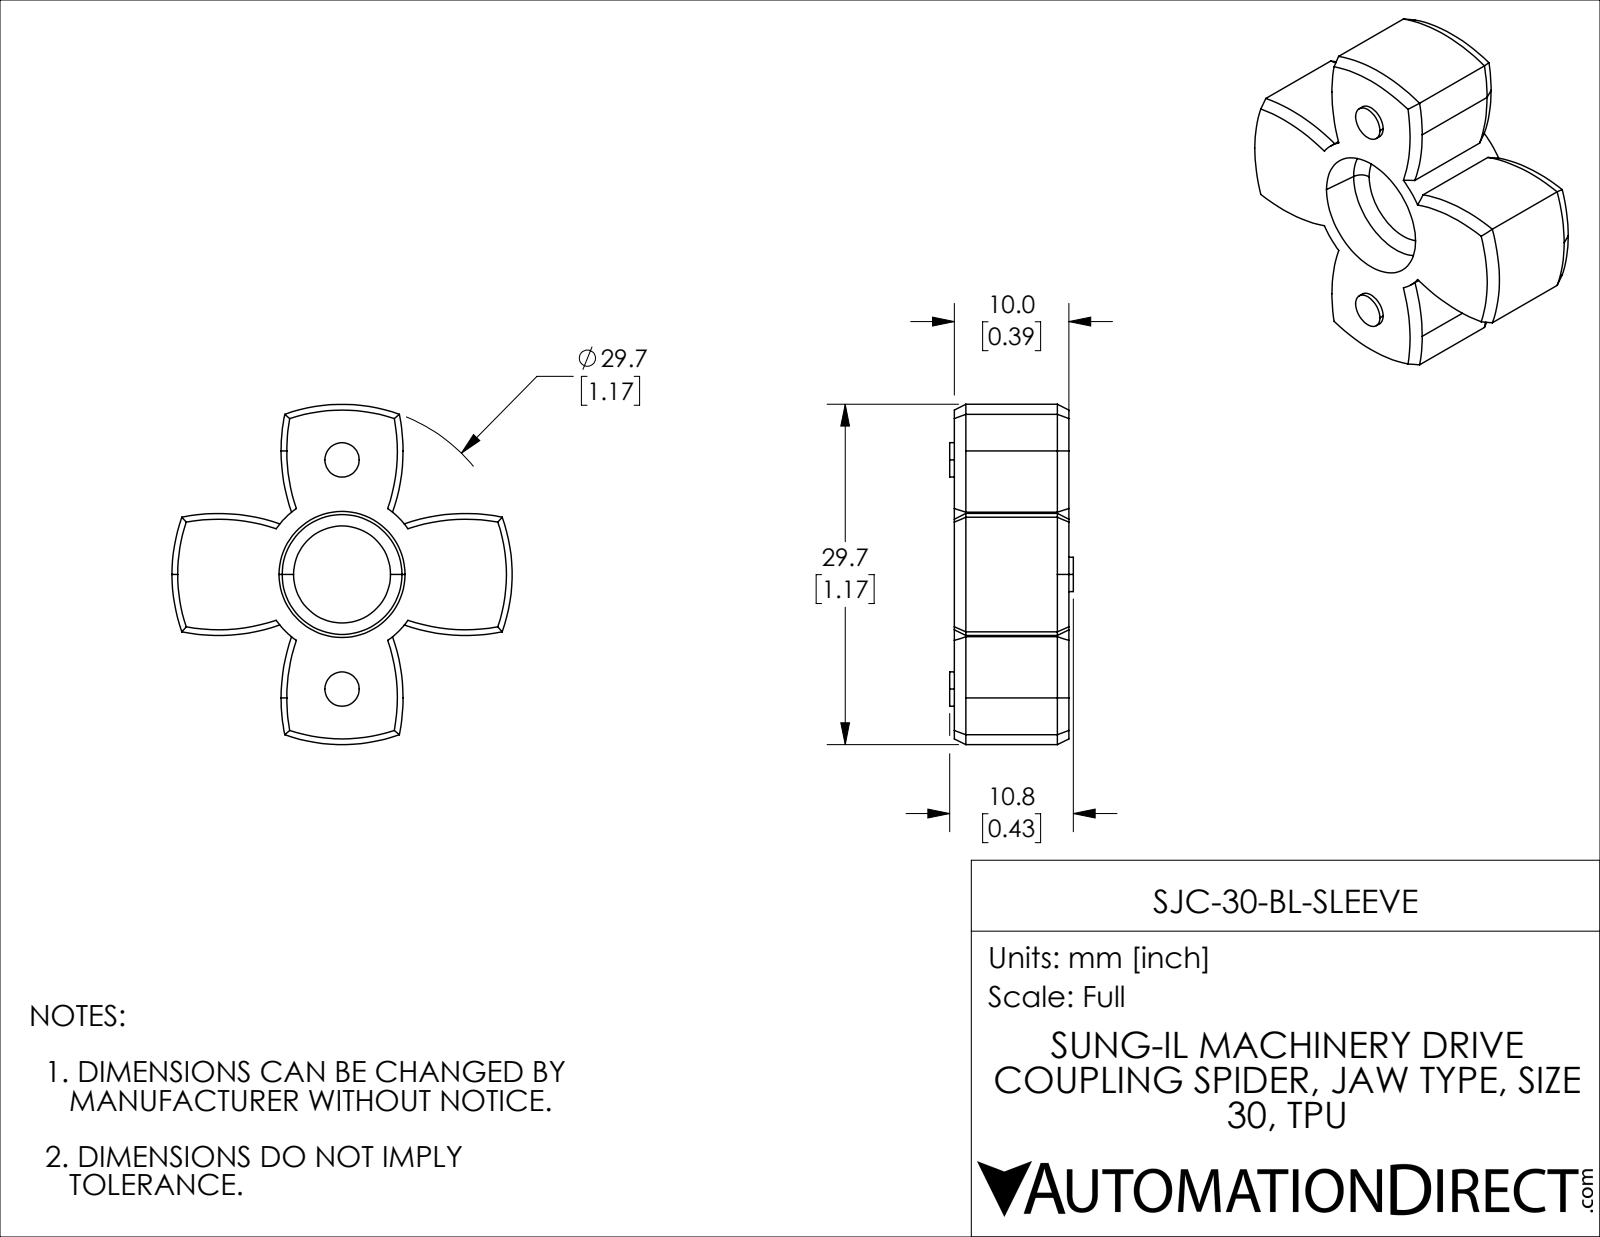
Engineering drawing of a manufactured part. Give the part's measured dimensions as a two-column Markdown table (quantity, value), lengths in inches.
| quantity | value |
| --- | --- |
| part name | SJC-30-BL-SLEEVE |
| STEP written by | SolidWorks 2021 (CONFIG_CONTROL_DESIGN) |
| units | inches |
| bodies | 1 solid, 73 faces (8 planar, 27 cylindrical, 38 other) |
| overall size | 1.169 × 1.169 × 0.425 |
| volume | 0.252 in³ |
| surface area | 3.545 in² |
| round bosses / shafts (diameter × count) | 0.118 × 4 |
| partial cylindrical surfaces (radius × count) | 0.634 × 4, 0.276 × 1, 0.585 × 1 |
| main face-to-face distances | 0.394, 0.157, 0.236, 0.079, 0.016, 0.173, 0.252, 0.409, 0.425 |
